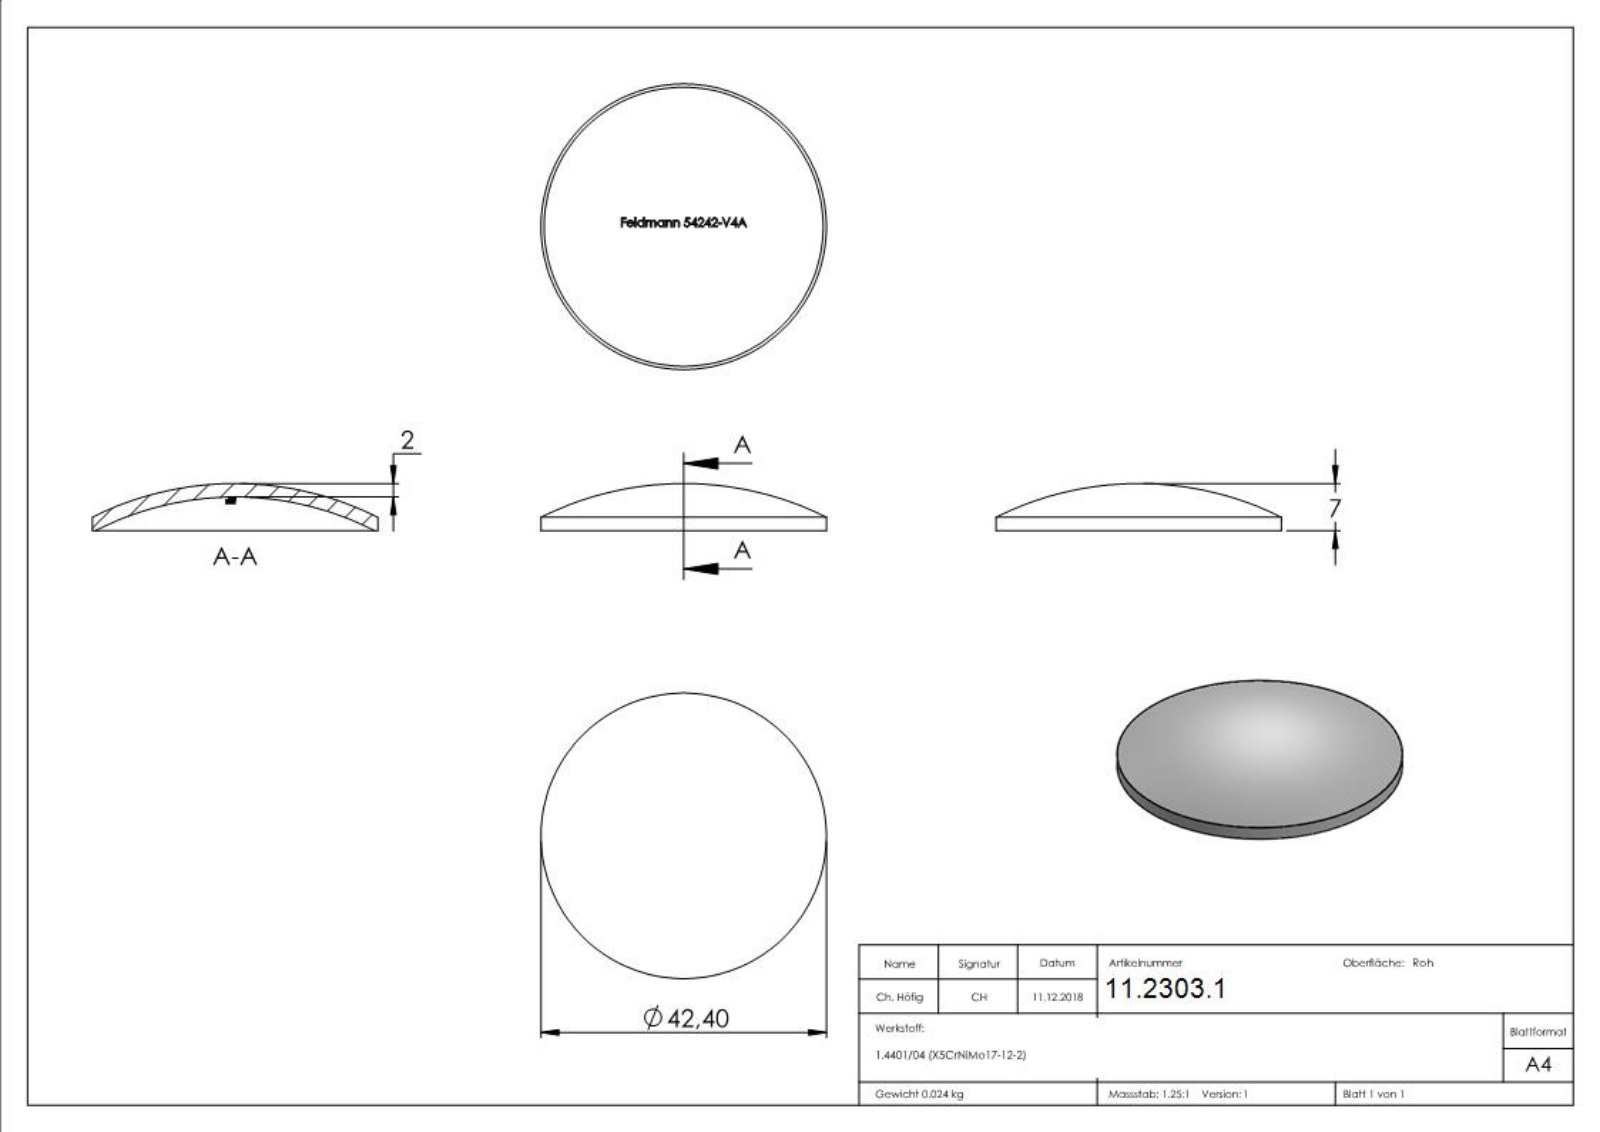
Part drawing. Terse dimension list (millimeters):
name: 54242-V4A
written by: SolidWorks 2015 (CONFIG_CONTROL_DESIGN)
unit: mm
bodies: 1 solid, 243 faces (134 planar, 2 cylindrical, 107 other)
size: 42.4 × 42.4 × 7
volume: 2 980 mm³; area: 3 257 mm²
bosses: 1× ⌀42.4
face distances: 0.44, 2.97, 0.39, 0.88, 2.01, 0.31, 1.26, 10.96, 5.97, 1.65
